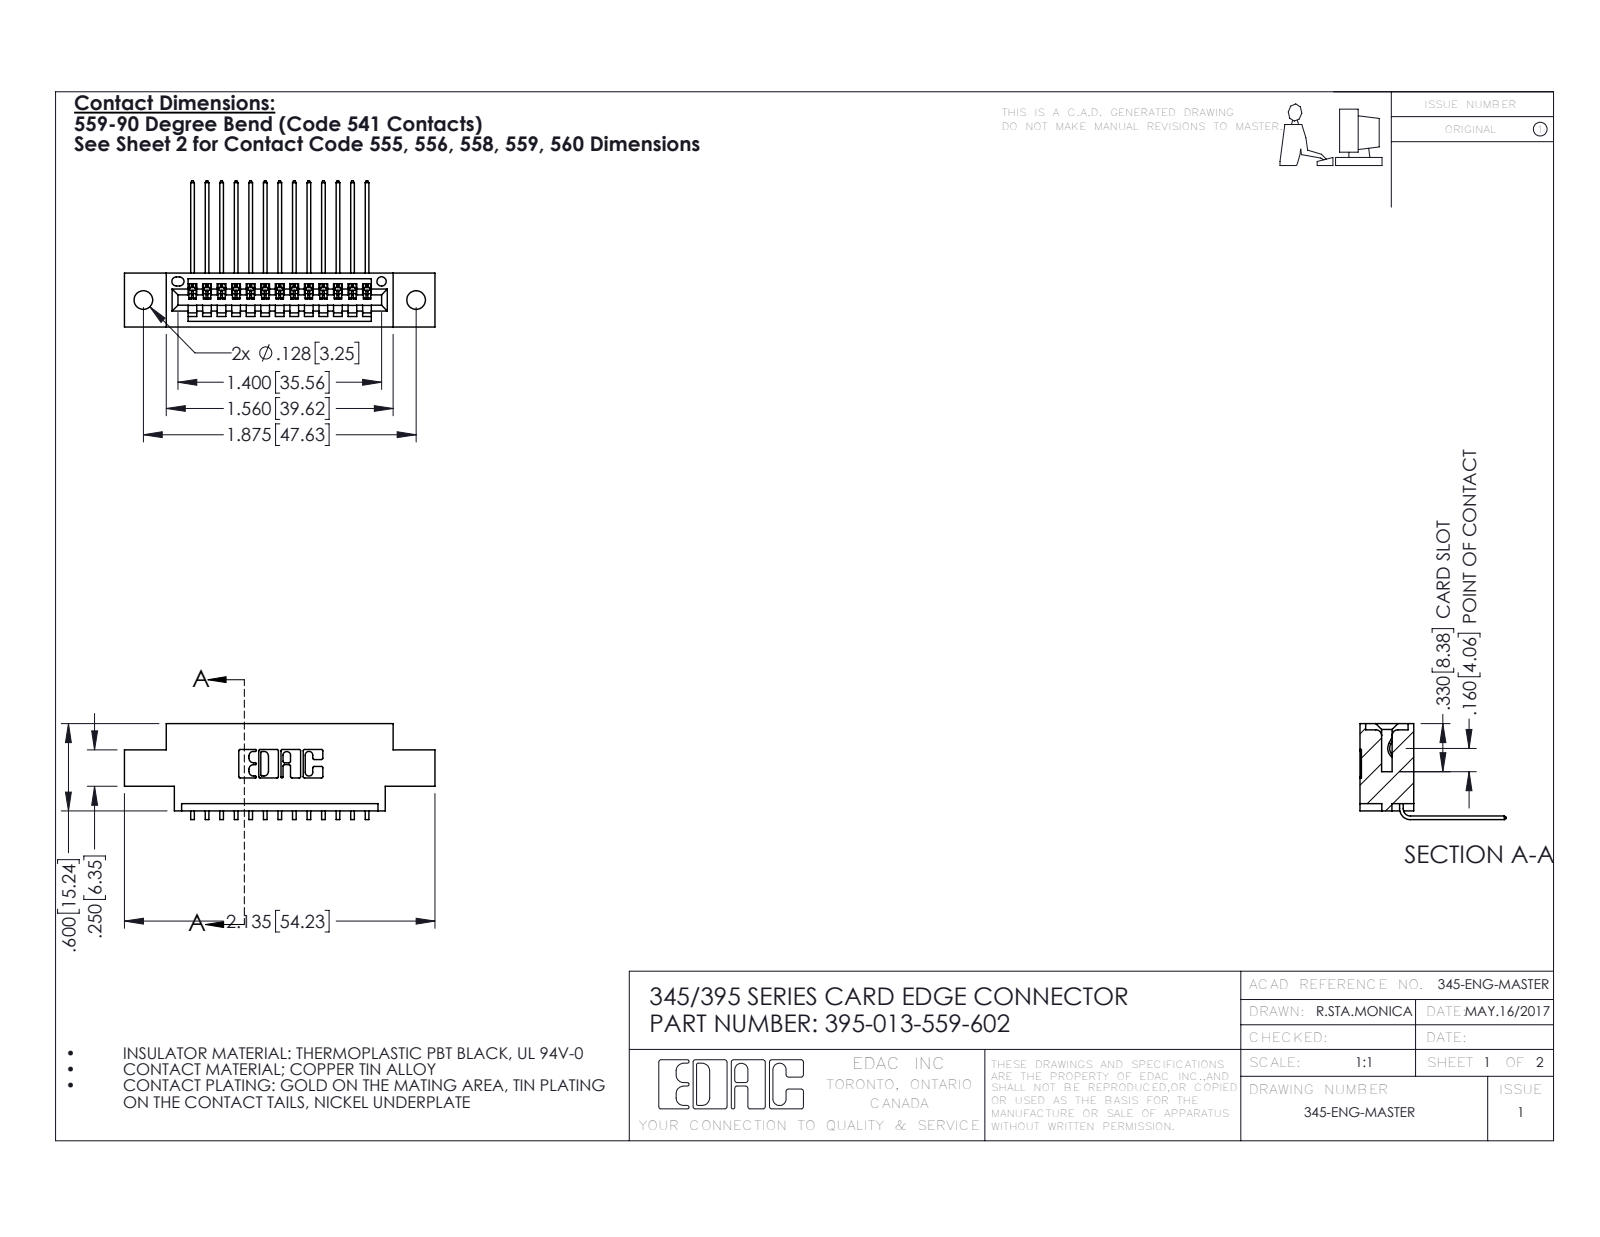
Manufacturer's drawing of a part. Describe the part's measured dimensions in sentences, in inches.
The part is named "345-292-001_558 559 Tail - 1; 395-013-559-602; 345 Part_0.170 Offset - 0.128 Dia". Its 3-D file was written by "SolidWorks 2016 (CONFIG_CONTROL_DESIGN)". It is 14 solids with 910 faces: 630 planar, 280 cylindrical and 0 other. Overall it measures 2.135 by 1.005 by 0.659 inches. Its volume is 0.293 cubic inches and its surface area 9.459 square inches. Round holes: 2 of diameter 0.128, 1 of diameter 0.064. Partial cylindrical surfaces (rounded edges, fillets, slot ends): 26 of radius 0.006, 22 of radius 0.01, 6 of radius 0.007, 6 of radius 0.031, 3 of radius 0.026, 2 of radius 0.031, 2 of radius 0.04, 1 of radius 0.014. The main face-to-face distances are 0.37, 0.072, 0.298, 0.2, 0.098, 0.272, 0.025, 0.1, 0.225, 0.15. The hole center spacings are 0.27, 1.643, 1.875.
